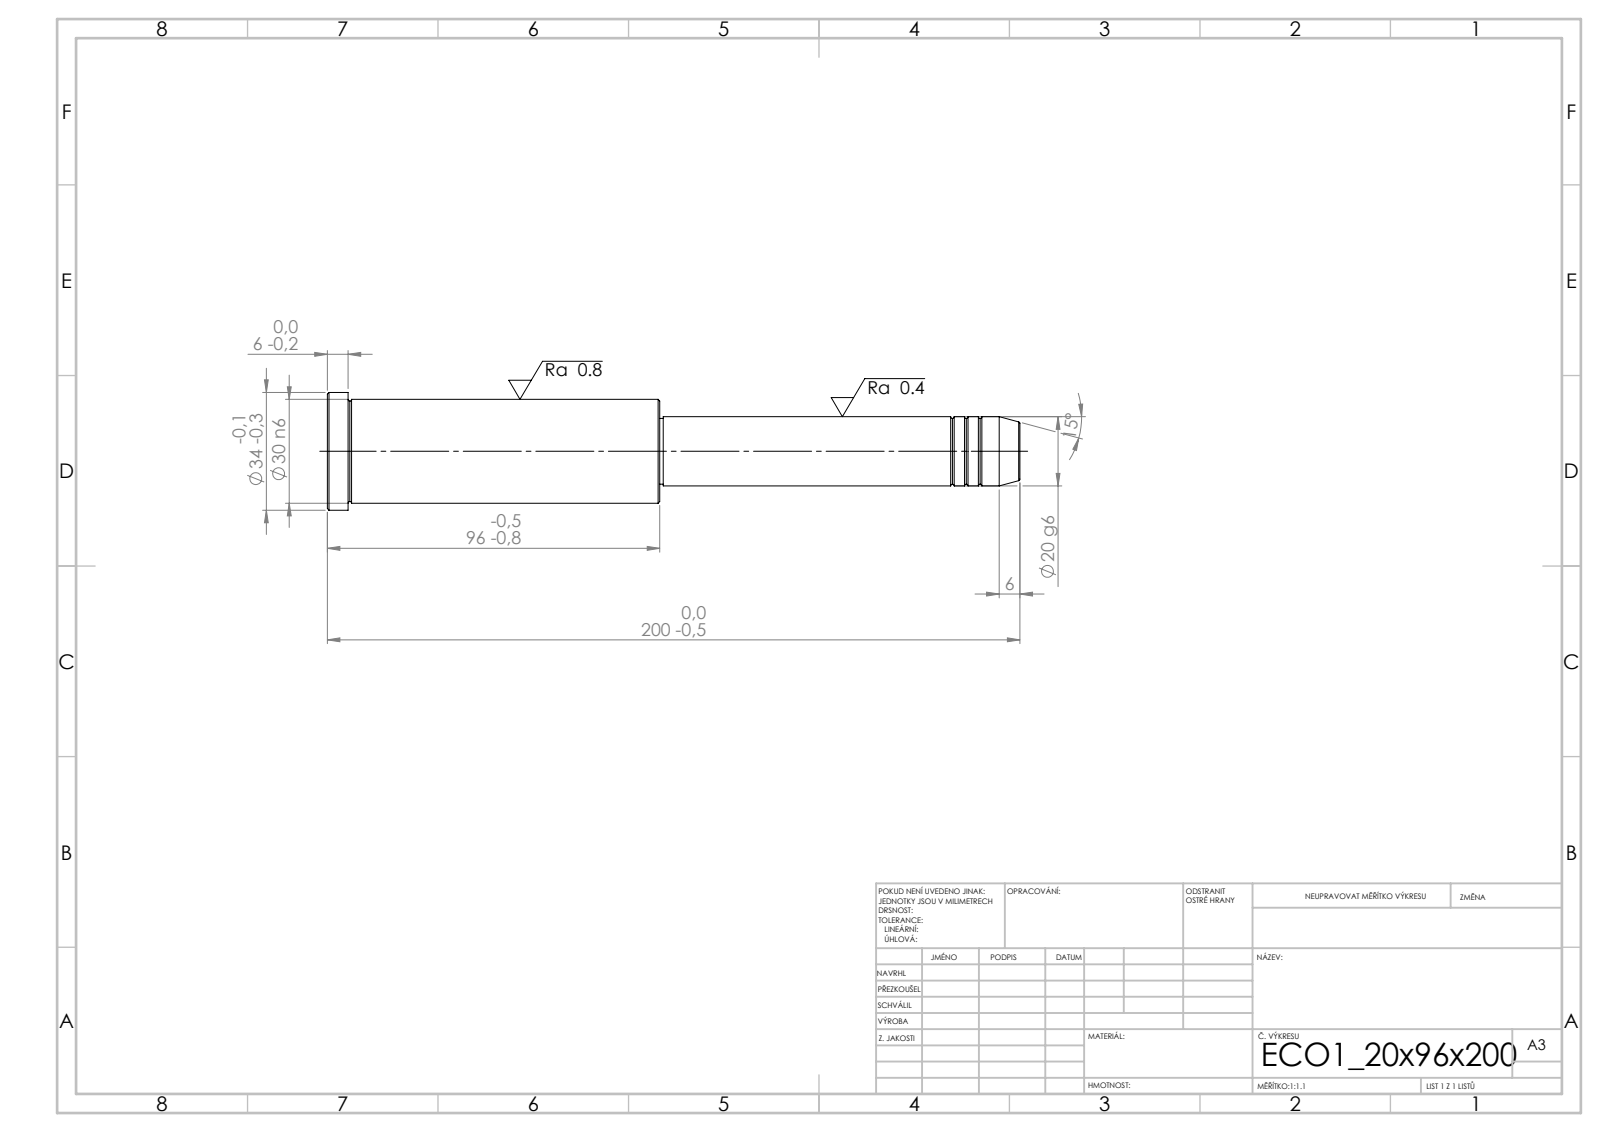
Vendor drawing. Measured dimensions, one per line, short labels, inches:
written by: SolidWorks 2019 (CONFIG_CONTROL_DESIGN)
unit: in
bodies: 1 solid, 43 faces (5 planar, 14 cylindrical, 24 other)
size: 7.874 × 1.339 × 1.339
volume: 6.181 in³; area: 27.13 in²
bosses: 1× ⌀1.339, 1× ⌀1.181, 1× ⌀0.787, 1× ⌀0.748
face distances: 3.78, 4.094, 7.874, 7.638, 3.543, 0.236, 4.055, 0.039, 3.583, 3.819
